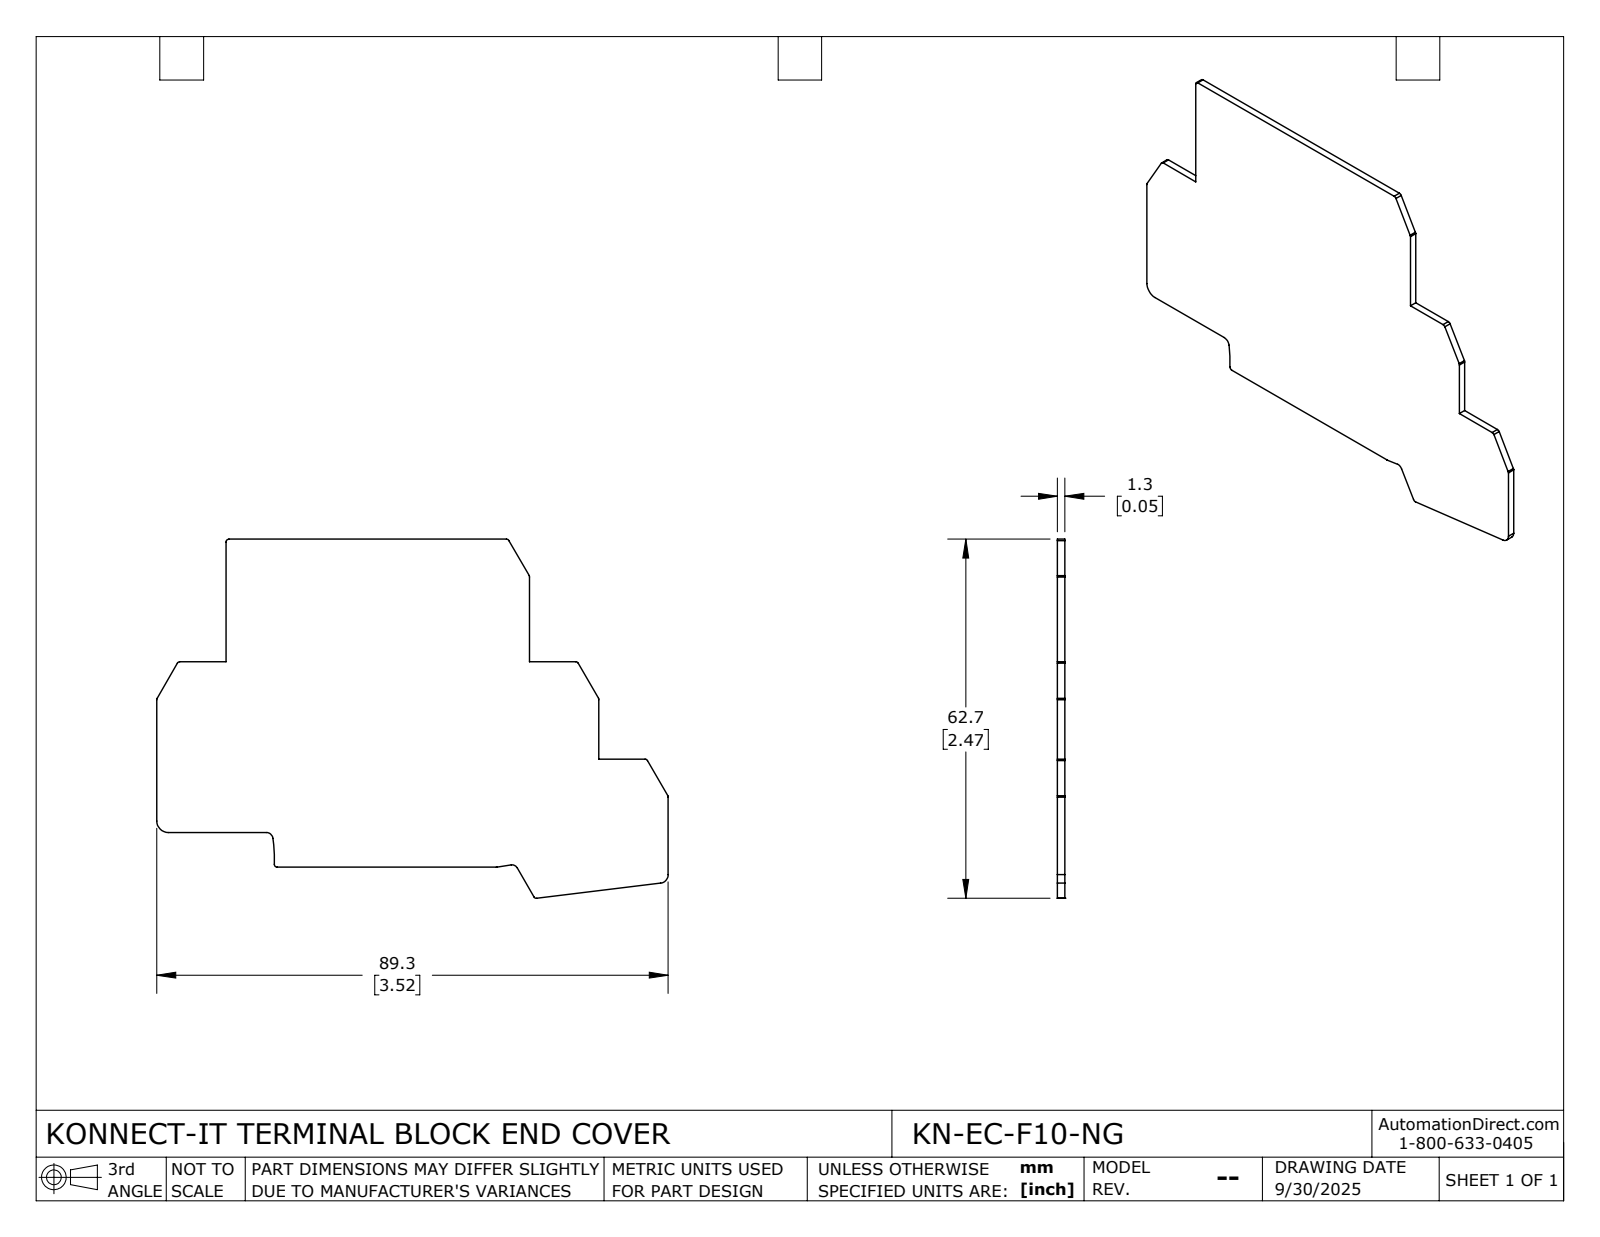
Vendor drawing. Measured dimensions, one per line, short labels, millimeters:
name: KN-EC-F10-NG
written by: SolidWorks 2024 (CONFIG_CONTROL_DESIGN)
unit: mm
bodies: 1 solid, 38 faces (20 planar, 18 cylindrical, 0 other)
size: 89.3 × 62.69 × 1.3
volume: 5 275 mm³; area: 8 487 mm²
rounds: 11× R0.5, 2× R1, 1× R1.2, 1× R1.5, 1× R2, 1× R30.7
face distances: 1.3, 12.1, 57.24, 65.1, 77.2, 6.05, 51.19, 35.84, 29.79, 21.4
